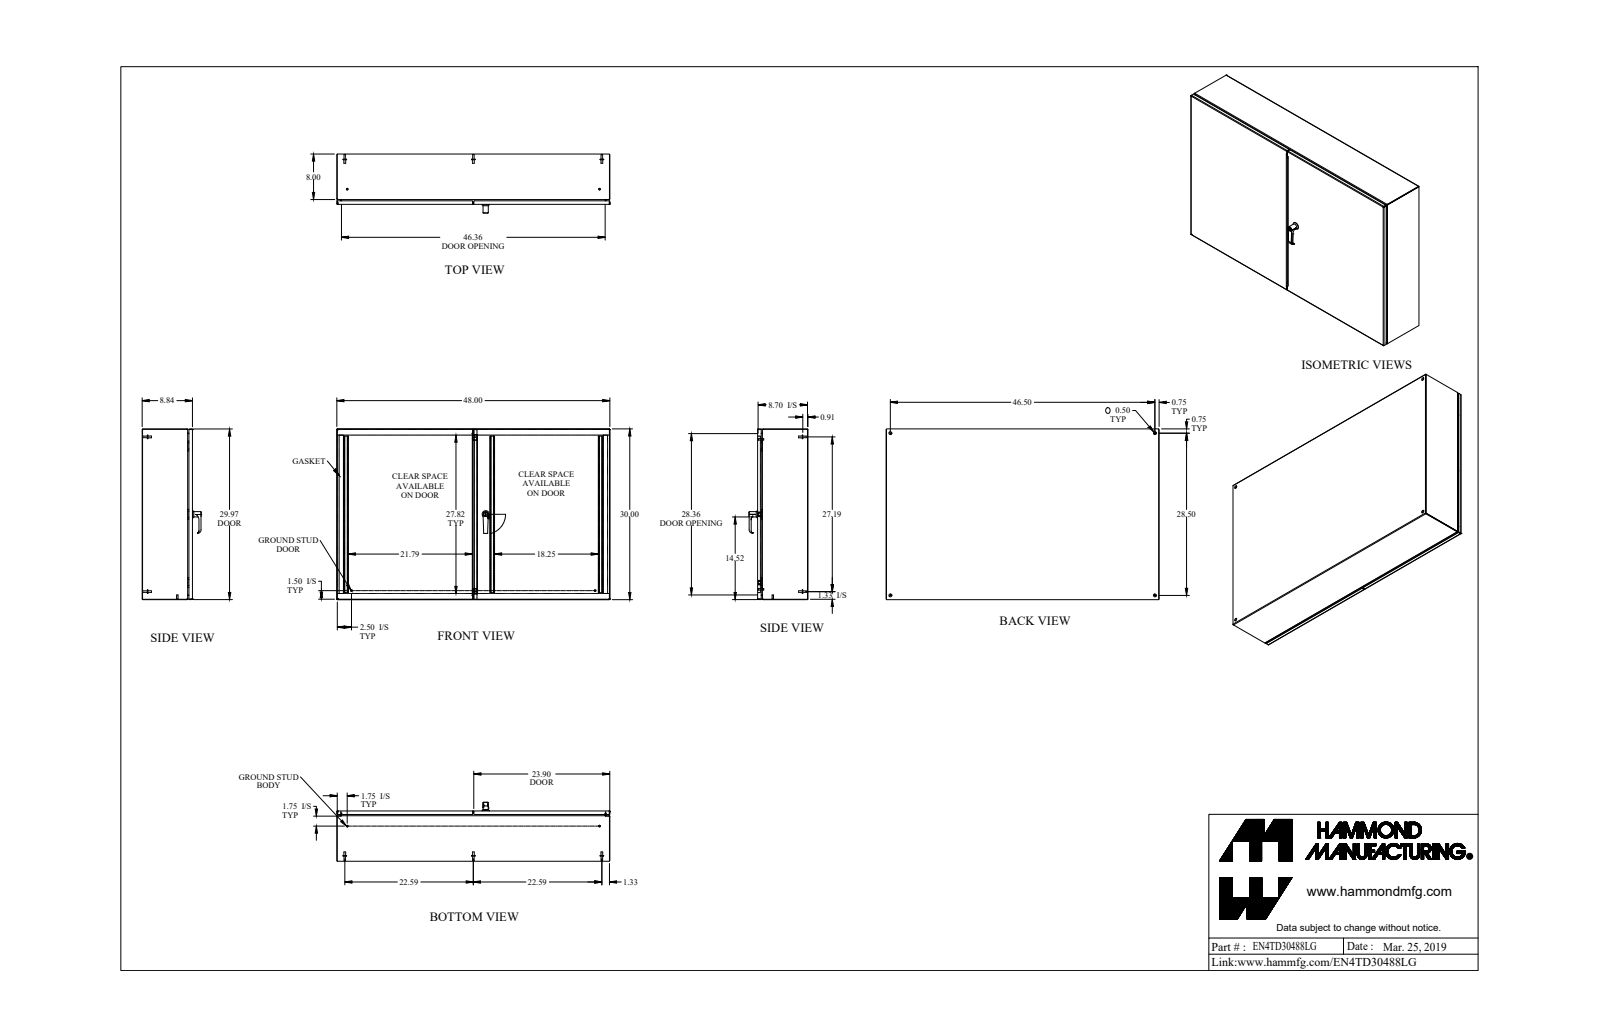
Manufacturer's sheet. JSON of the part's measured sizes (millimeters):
{"part_name": "EN4TD30488LG", "step_written_by": "SolidWorks 2018 (AUTOMOTIVE_DESIGN)", "units": "millimeters", "bodies": {"solids": 85, "faces": 2139, "planar": 955, "cylindrical": 790, "other": 394}, "overall_size": [1219.2, 762, 263.4], "volume_mm3": 6168000, "surface_area_mm2": 6352000, "round_holes": [[5, 5], [4.5, 4], [6.7, 4], [12.7, 4], [6.1, 3], [6.1, 3], [4.4, 2], [6.4, 2], [6.5, 2], [6.6, 2], [8, 2], [10, 2]], "round_bosses_or_shafts": [[6.4, 12], [8, 8], [15.9, 6], [6.9, 6], [13, 4], [7.1, 4], [4, 4], [19.1, 3]], "partial_cylinders_radius": [[0.9, 26], [2.7, 26], [2.4, 20], [1.1, 18], [2.1, 18], [1.6, 17], [0.5, 16], [1.6, 16]], "face_to_face_distances": [1.8, 222.8, 220.9, 224.6, 760.2, 1217.4, 758.3, 762, 1215.5, 1219.2], "hole_center_spacings": [20, 335, 528.3, 646.4, 654.1, 723.9, 740.1, 1181.1]}
